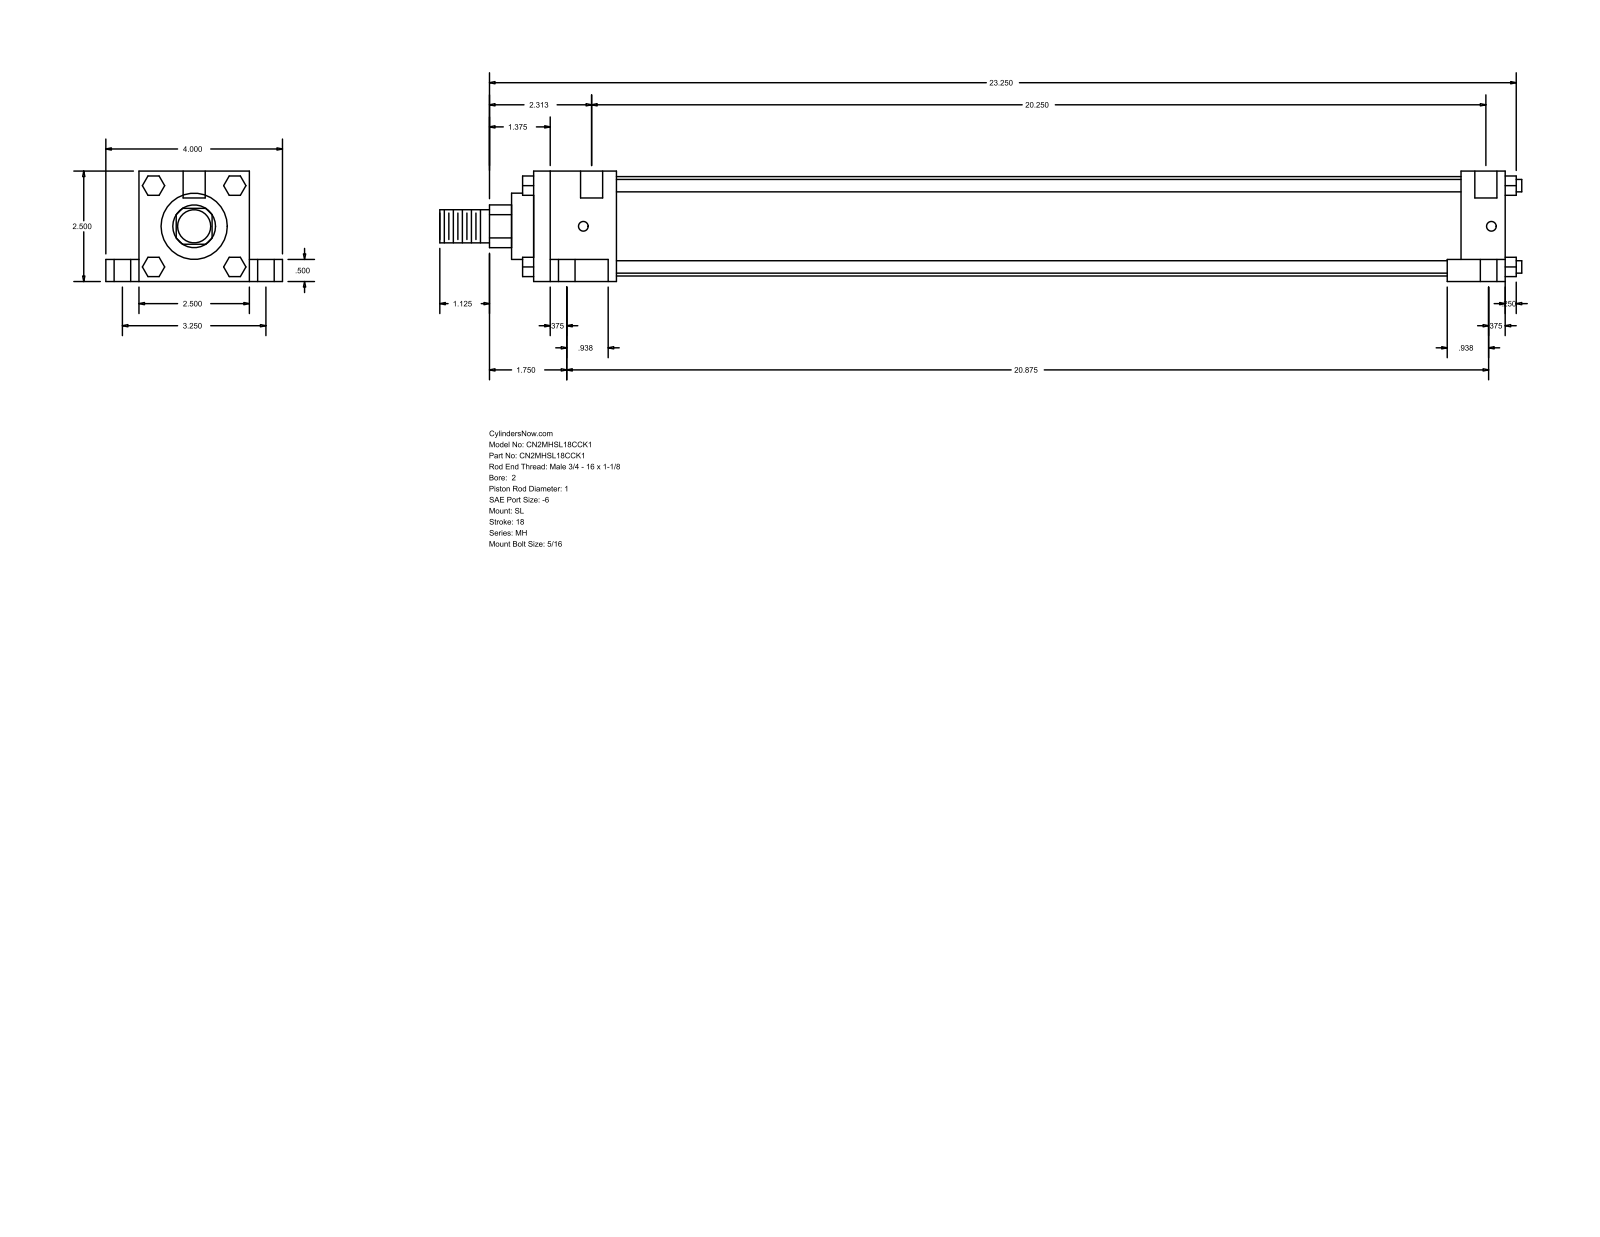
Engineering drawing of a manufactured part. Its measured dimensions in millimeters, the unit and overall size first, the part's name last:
Units: millimetres
Overall size (bounding box): 622.3 × 101.6 × 63.5
Round holes (diameter × count): ⌀5.56 ×4, ⌀9.53 ×4, ⌀15.88 ×4, ⌀12.7 ×2
Round bosses / shafts (diameter × count): ⌀7.14 ×4, ⌀57.15 ×1, ⌀38.1 ×1, ⌀25.4 ×1, ⌀19.05 ×1
Partial cylindrical surfaces — rounded edges, fillets, slot ends (radius × count): R12.29 ×1
Main face-to-face distances: 63.5, 558.8, 12.7, 19.05, 50.8, 82.55, 25.4, 533.4, 47.63, 485.77
Hole centre spacings: 41.3, 42.36, 43.67, 82.54, 517.58, 522.28, 522.32, 530.22
Bodies: 0 solids, 148 faces (112 planar, 36 cylindrical, 0 other)
Part name (STEP PRODUCT): MH_SL__0200_1
STEP written by: GSSL Pune (CONFIG_CONTROL_DESIGN)
